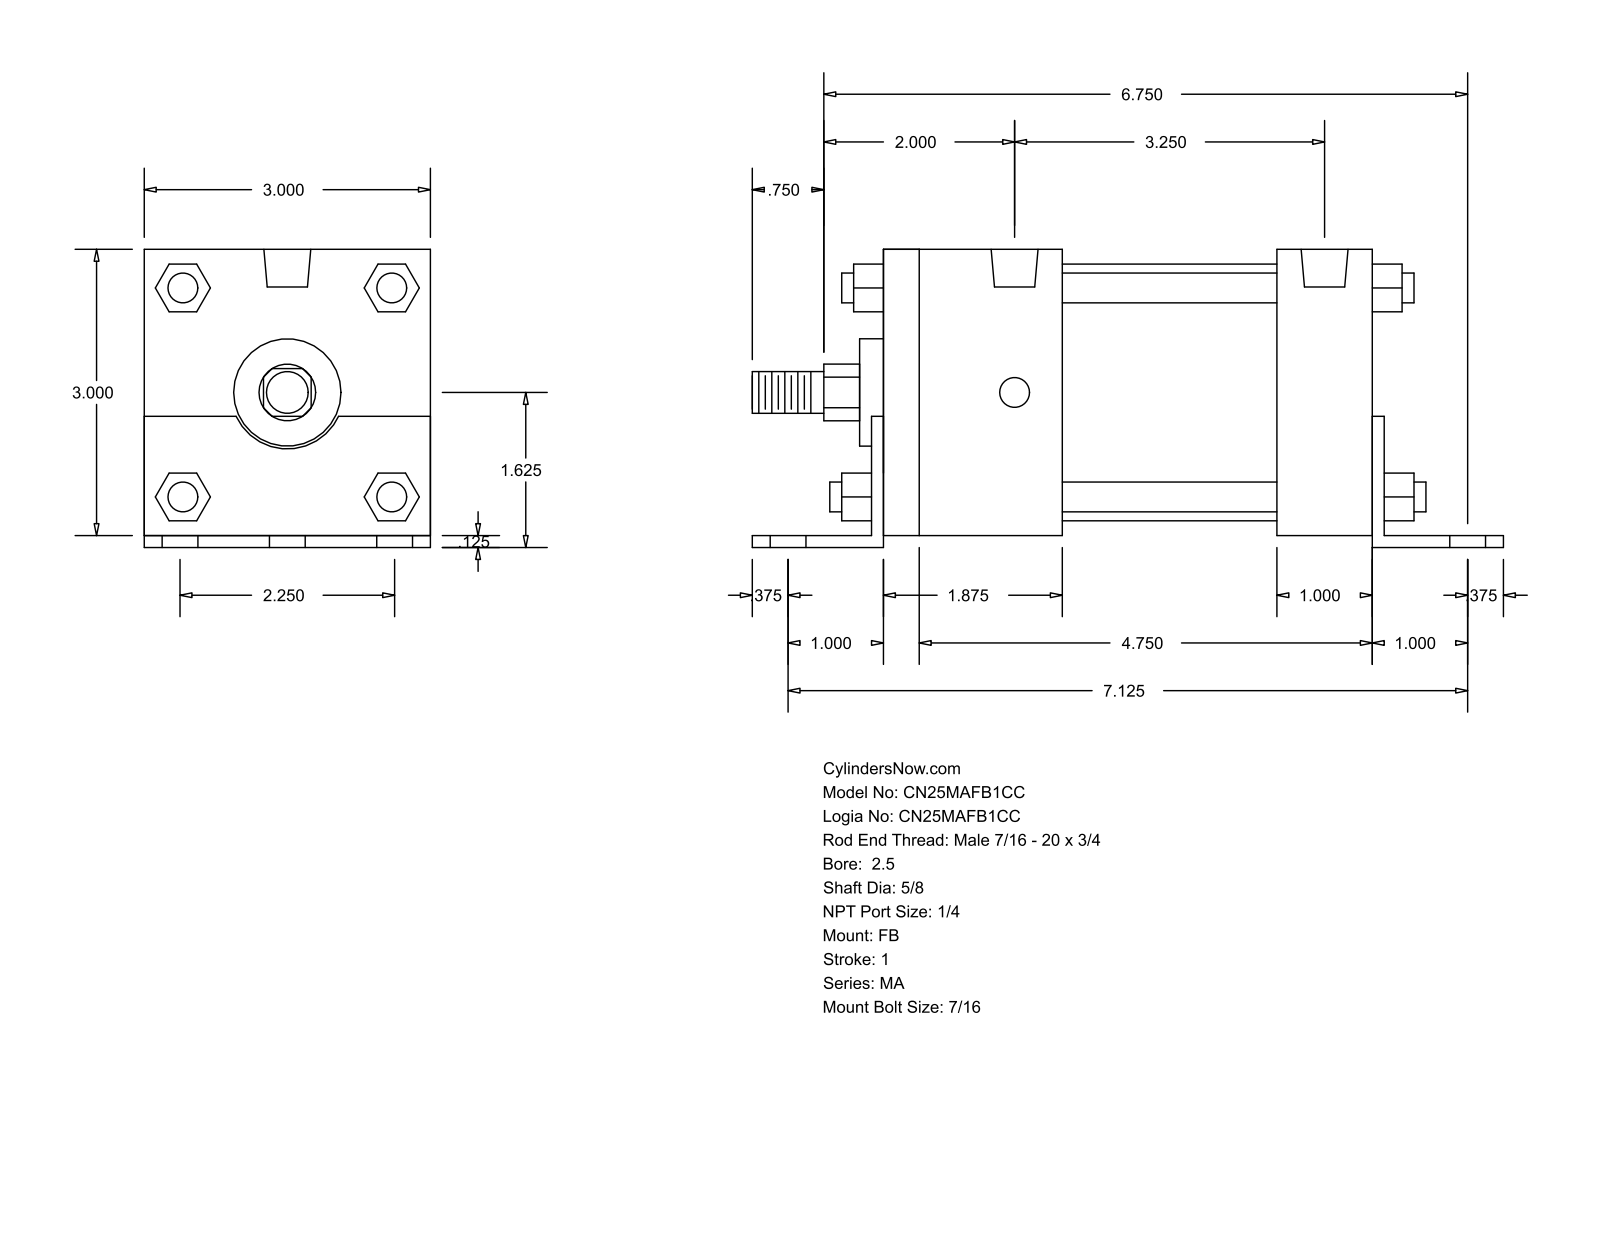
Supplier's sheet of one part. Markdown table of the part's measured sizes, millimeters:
| quantity | value |
| --- | --- |
| part name | MA_FB__0250_0.625 |
| STEP written by | GSSL Pune (CONFIG_CONTROL_DESIGN) |
| units | millimeters |
| bodies | 0 solids, 140 faces (105 planar, 35 cylindrical, 0 other) |
| overall size | 200.03 × 79.38 × 76.2 |
| round holes (diameter × count) | 11.11 × 6, 7.94 × 4, 12.49 × 2 |
| round bosses / shafts (diameter × count) | 7.94 × 4, 68.33 × 1, 28.57 × 1, 15.88 × 1, 11.11 × 1 |
| partial cylindrical surfaces (radius × count) | 7.54 × 1, 15.05 × 1 |
| main face-to-face distances | 76.2, 3.17, 79.37, 130.17, 136.52, 3.18, 82.55, 133.34, 47.62, 25.4 |
| hole center spacings | 28.57, 183.22, 180.98, 47.62, 57.14, 66.75, 82.55, 123.99 |
